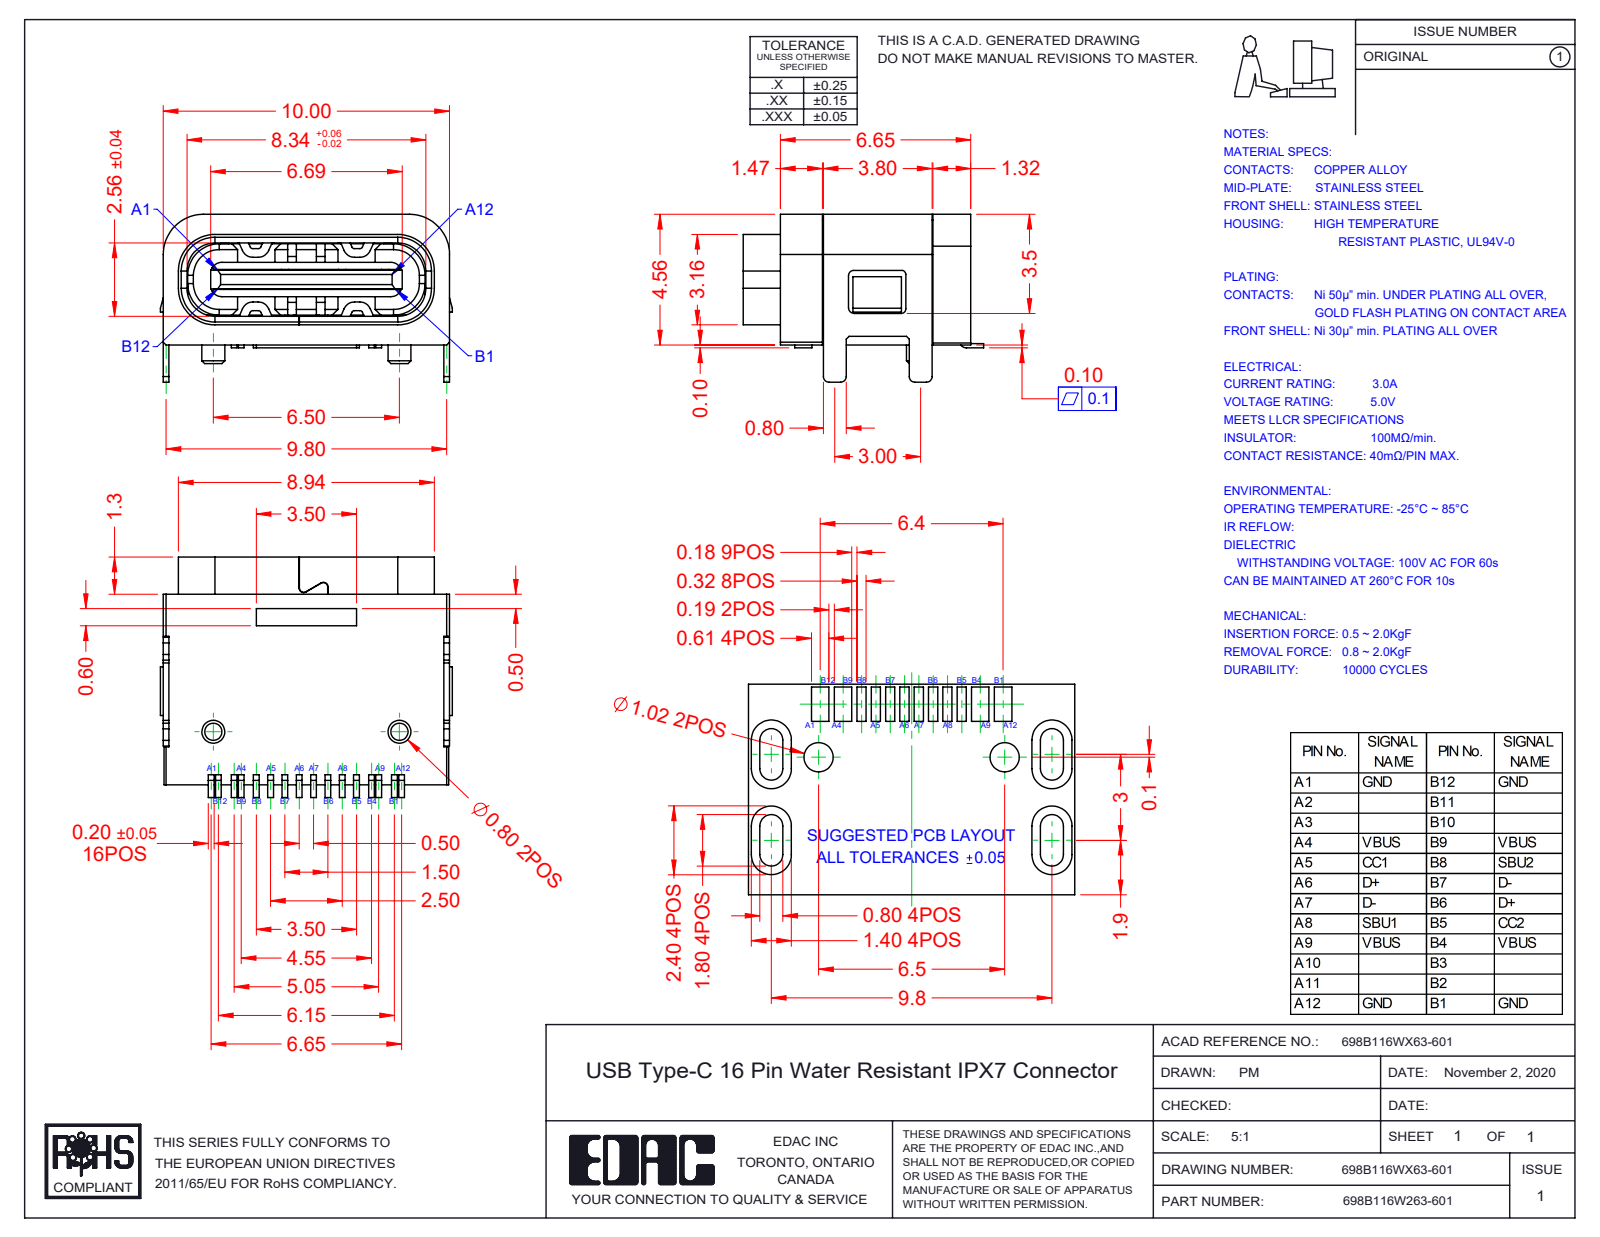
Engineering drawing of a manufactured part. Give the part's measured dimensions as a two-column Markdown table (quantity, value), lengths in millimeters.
| quantity | value |
| --- | --- |
| part name | Shell2 698B116WX63-601; 698B116W163-601; 698B116WX63-601 (Seal); Shell1 698B116WX63-601 (+1 more) |
| STEP written by | SolidWorks 2020 (AUTOMOTIVE_DESIGN) |
| units | millimeters |
| bodies | 4 solids, 633 faces (449 planar, 164 cylindrical, 20 other) |
| overall size | 10.64 × 8.7 × 6.01 |
| volume | 284 mm³ |
| surface area | 1 000 mm² |
| round bosses / shafts (diameter × count) | 0.8 × 2 |
| partial cylindrical surfaces (radius × count) | 0.15 × 27, 0.4 × 12, 0.5 × 10, 0.1 × 8, 0.2 × 8, 0.35 × 8, 0.16 × 7, 0.98 × 4 |
| main face-to-face distances | 0.7, 3.86, 0.5, 1, 3.56, 2.86, 3.16, 3.66, 4.36, 0.8 |
